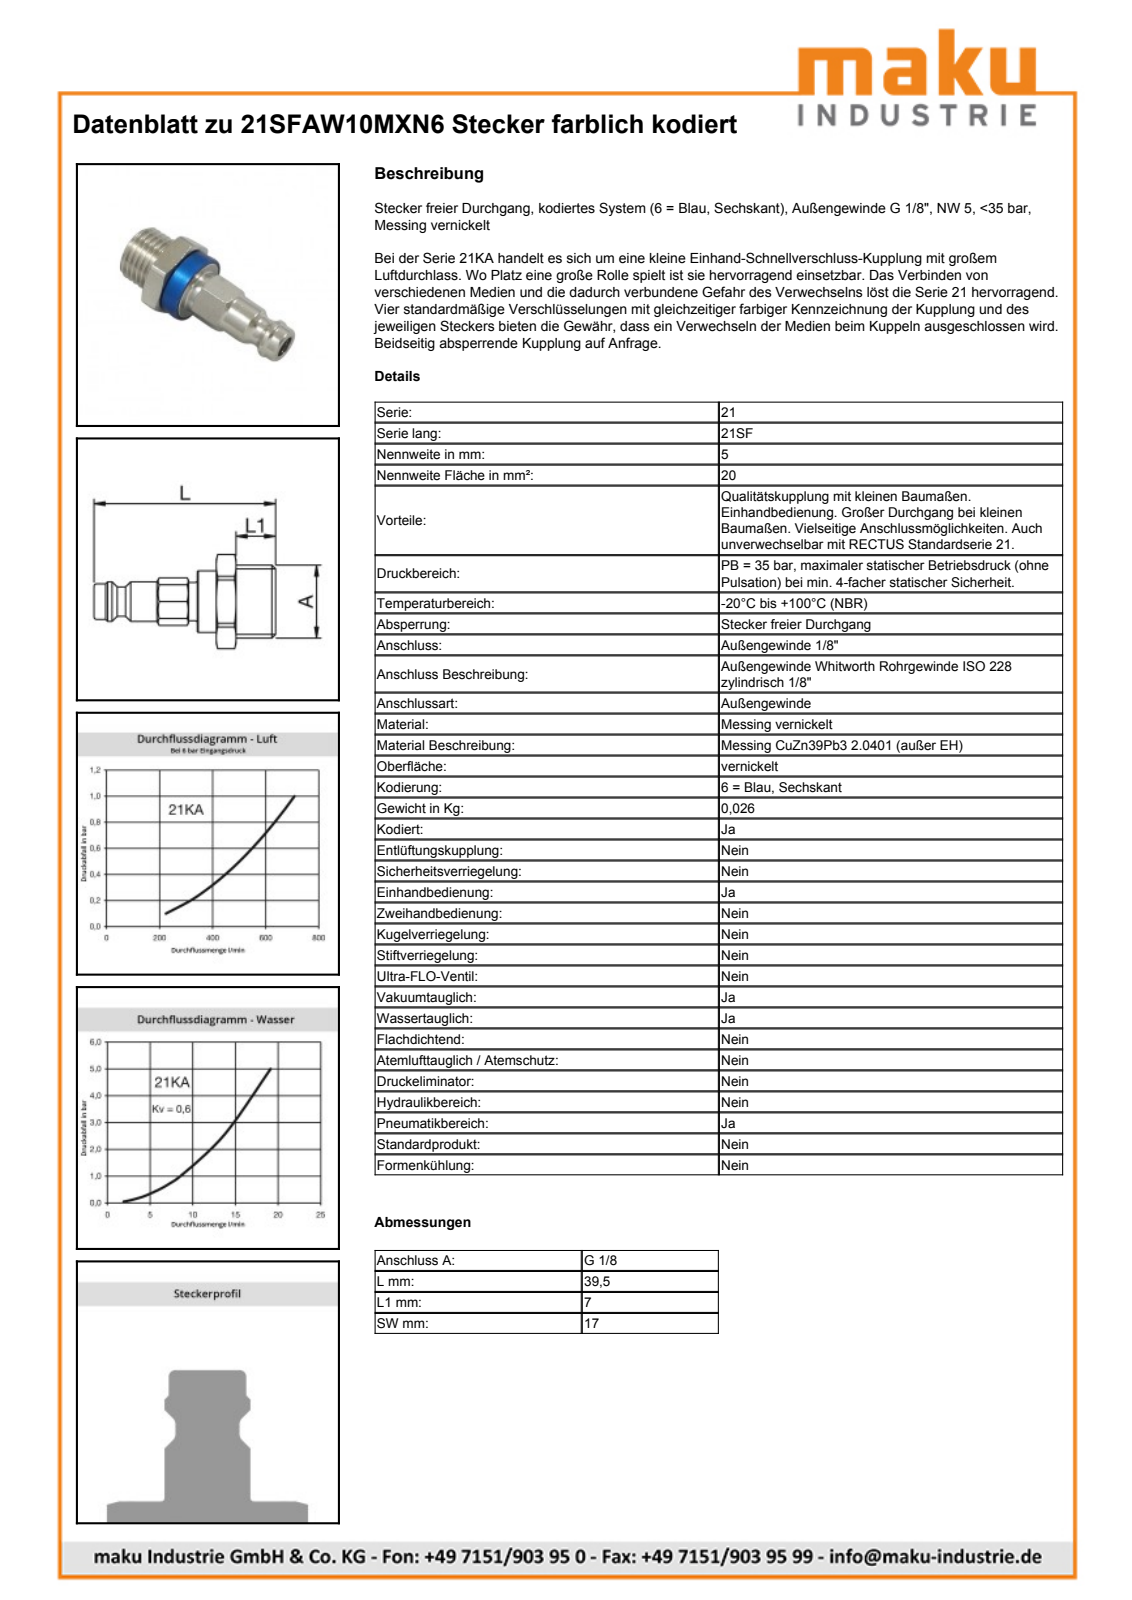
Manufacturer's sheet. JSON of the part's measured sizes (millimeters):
{"part_name": "D110186; D110094; D104771", "step_written_by": "Autodesk Inventor 2020 (AUTOMOTIVE_DESIGN)", "units": "millimeters", "bodies": {"solids": 2, "faces": 69, "planar": 19, "cylindrical": 23, "other": 27}, "overall_size": [39.5, 19, 17], "volume_mm3": 3230, "surface_area_mm2": 2853, "round_holes": [[4.95, 1], [13.85, 1], [14.05, 1]], "round_bosses_or_shafts": [[15.5, 1], [14, 1], [9.73, 1], [9.7, 1], [9, 1], [8.1, 1], [6.65, 1]], "partial_cylinders_radius": [[5.7, 1], [9.5, 1]], "face_to_face_distances": [3.5, 13.5, 4.5, 10, 17, 9, 4.2, 8.7, 23.5, 23.8]}
